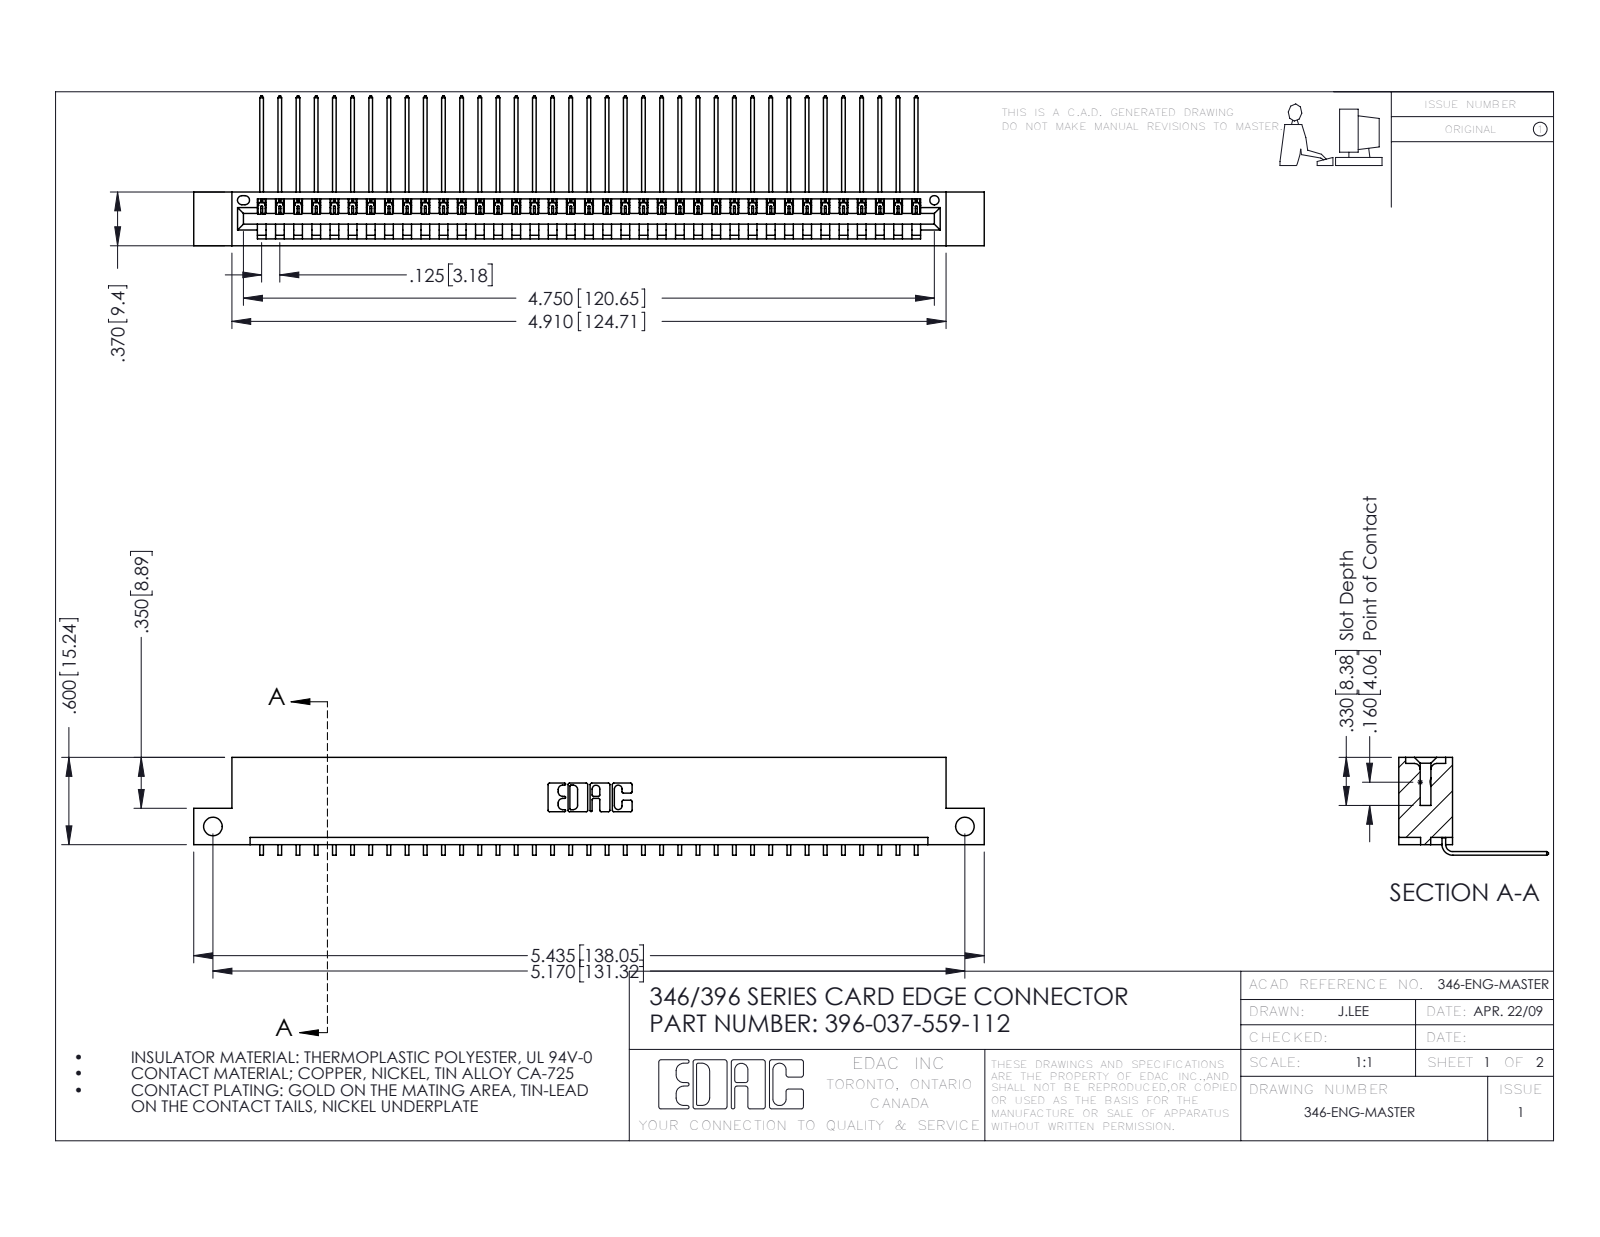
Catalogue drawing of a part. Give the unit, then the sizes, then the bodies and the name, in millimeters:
Units: millimetres
Overall size (bounding box): 138 × 26.2 × 17.1
Round holes (diameter × count): ⌀3.3 ×2, ⌀1.6 ×1
Partial cylindrical surfaces — rounded edges, fillets, slot ends (radius × count): R0.2 ×74, R0.3 ×22, R0.2 ×6, R0.8 ×6, R0.7 ×3, R0.8 ×2, R1 ×2, R0.4 ×1
Main face-to-face distances: 1.2, 8.2, 9.4, 6.4, 1.8, 0.6, 7.6, 3.8, 5.6, 2.5
Hole centre spacings: 131.3
Volume: 13 200 mm³ · Surface area: 17 050 mm²
Bodies: 38 solids, 2342 faces (1630 planar, 712 cylindrical, 0 other)
Part name (STEP PRODUCT): 346 Part_Flush Mounting Lugs - Side Mount; 345-292-001_558 559 Tail - 1; 396-037-559-112
STEP written by: SolidWorks 2016 (CONFIG_CONTROL_DESIGN)
